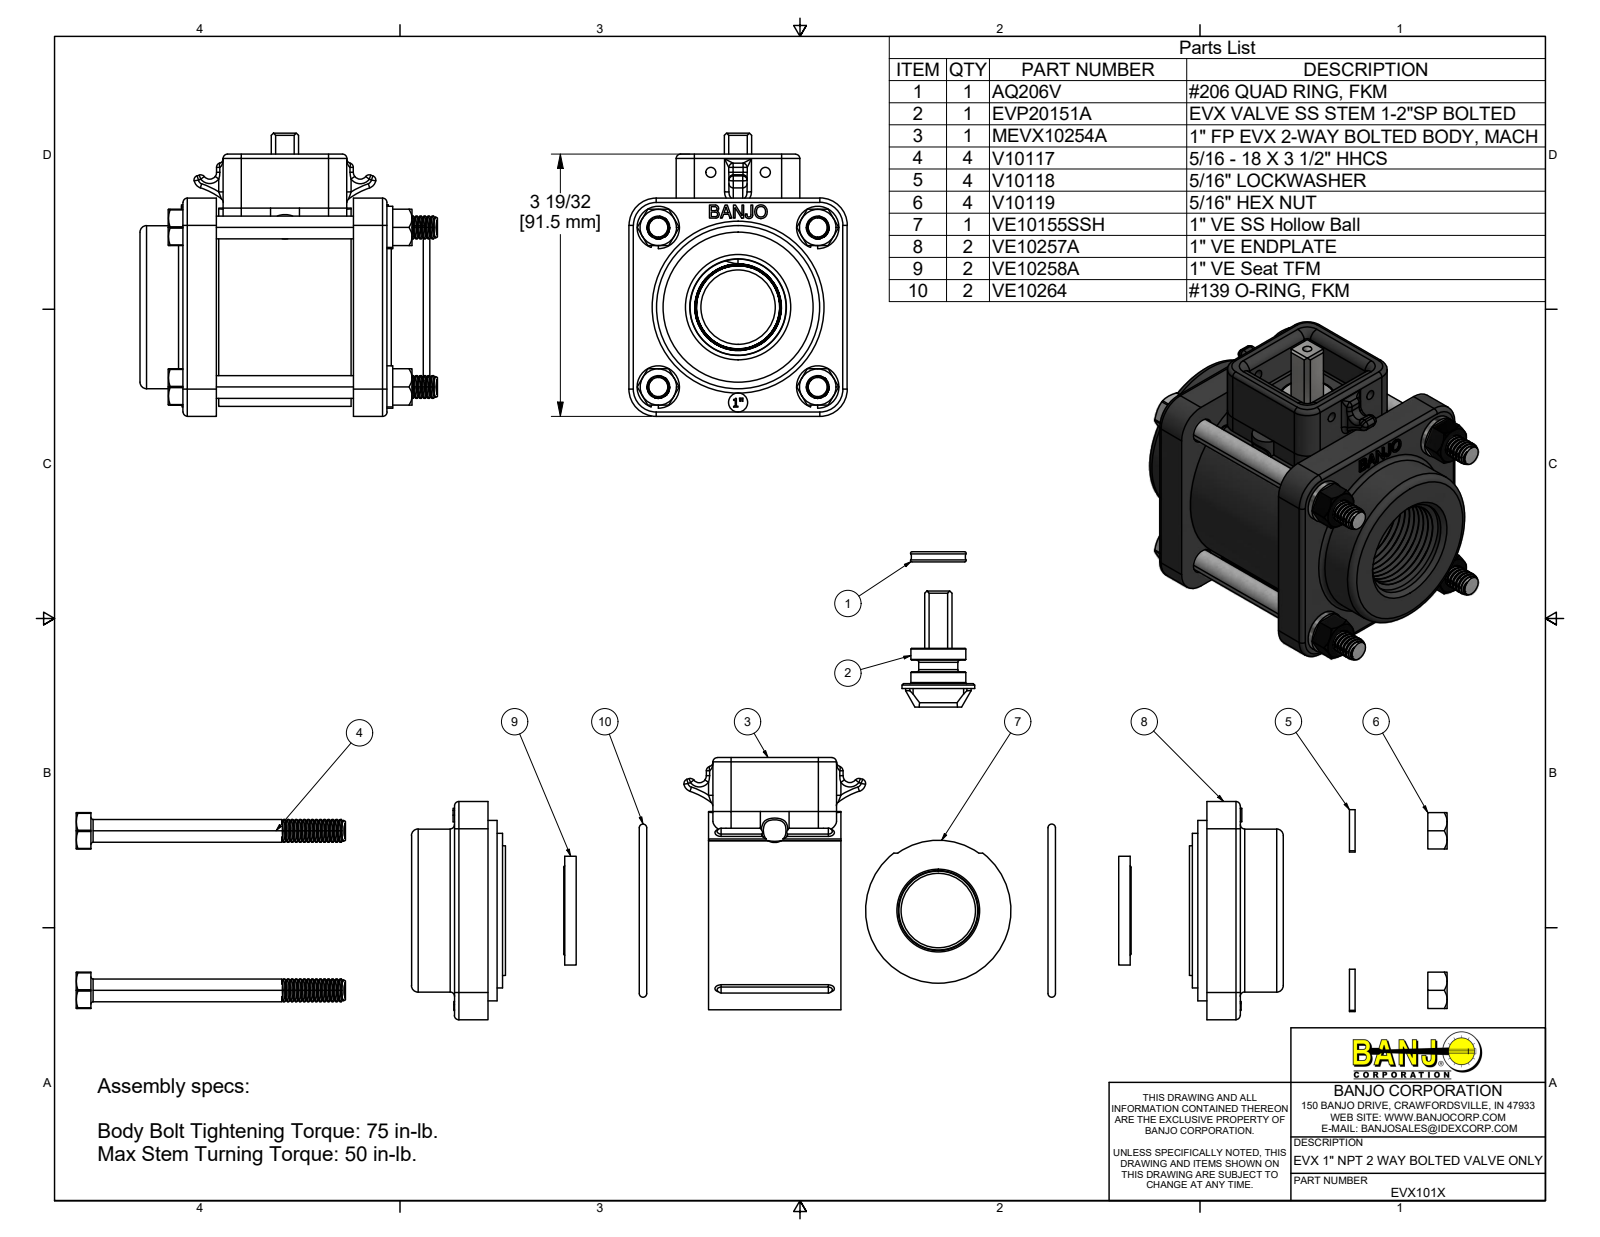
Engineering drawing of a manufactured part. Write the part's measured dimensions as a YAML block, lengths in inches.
part_name: "EVX101X; MEVX10254A; MEVX10254AX; VE10155SSH (+8 more)"
step_written_by: "Autodesk Inventor 2019 (AUTOMOTIVE_DESIGN)"
units: inches
bodies: {solids: 22, faces: 1535, planar: 362, cylindrical: 524, other: 649}
overall_size: [38.771, 3.893, 3]
volume: 19.05
surface_area: 343.7
round_holes:
  - {diameter: 0.252, count: 4}
  - {diameter: 0.322, count: 4}
  - {diameter: 0.35, count: 4}
  - {diameter: 1.02, count: 3}
  - {diameter: 0.135, count: 2}
  - {diameter: 0.26, count: 1}
  - {diameter: 0.76, count: 1}
  - {diameter: 1.5, count: 1}
  - {diameter: 2.12, count: 1}
  - {diameter: 2.375, count: 1}
  - {diameter: 2.5, count: 1}
round_bosses_or_shafts:
  - {diameter: 0.268, count: 60}
  - {diameter: 0.583, count: 4}
  - {diameter: 0.313, count: 4}
  - {diameter: 2.725, count: 1}
  - {diameter: 2.48, count: 1}
  - {diameter: 2.24, count: 1}
  - {diameter: 2.124, count: 1}
  - {diameter: 1.495, count: 1}
partial_cylinders:
  - {radius: 0.06, count: 58}
  - {radius: 0.03, count: 12}
  - {radius: 0.134, count: 8}
  - {radius: 0.375, count: 7}
  - {radius: 0.125, count: 6}
  - {radius: 0.21, count: 4}
  - {radius: 0.25, count: 4}
  - {radius: 0.284, count: 4}
face_to_face_distances: [0.46, 2.345, 2.805, 1.885, 3, 0.125, 0.59, 1.05, 2.935, 3.395]
hole_center_spacings: [1.55, 2.192, 1.046, 1.117, 1.891, 2.644, 3.1, 3.186]
